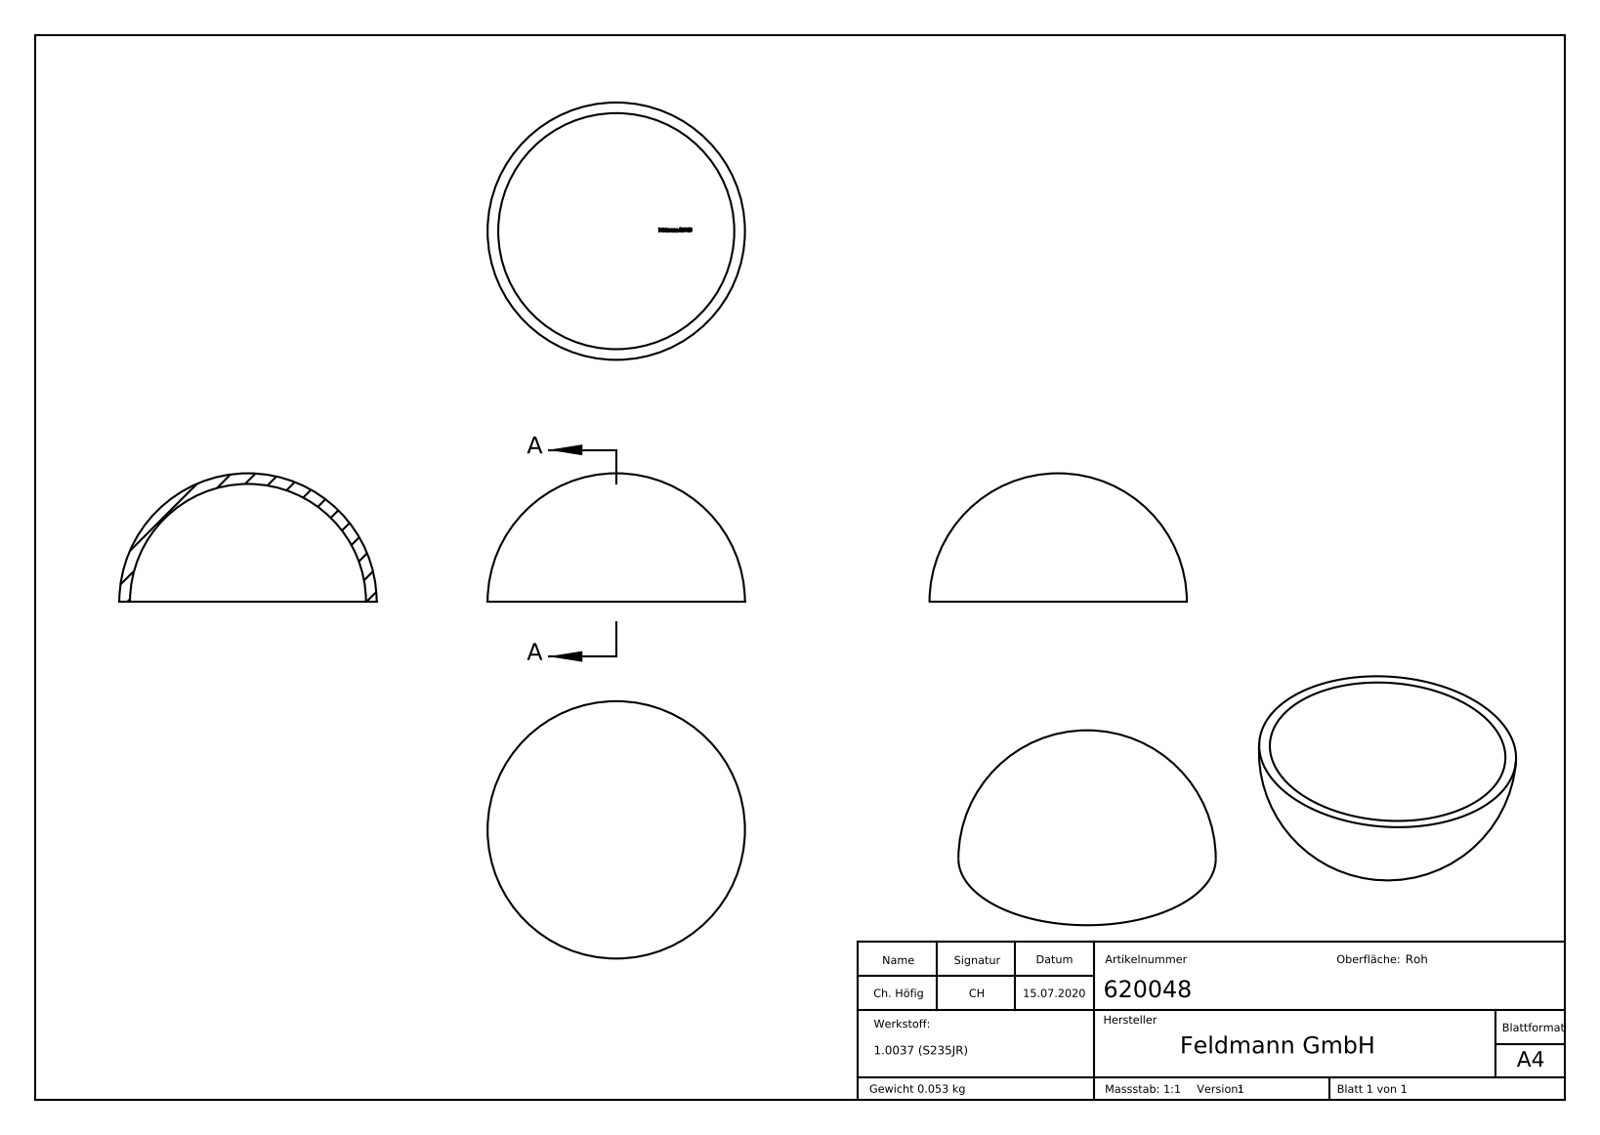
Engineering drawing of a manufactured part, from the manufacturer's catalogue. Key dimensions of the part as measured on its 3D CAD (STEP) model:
Part name (STEP PRODUCT): 620048
STEP written by: SolidWorks 2018 (CONFIG_CONTROL_DESIGN)
Units: millimetres
Bodies: 1 solid, 200 faces (77 planar, 0 cylindrical, 123 other)
Overall size (bounding box): 48.3 × 48.3 × 24.15
Volume: 6 739 mm³ · Surface area: 7 042 mm²
Main face-to-face distances: 0.45, 3.1, 4.79, 2.65, 0.61, 1.19, 2.54, 0.55, 0.5, 0.81
